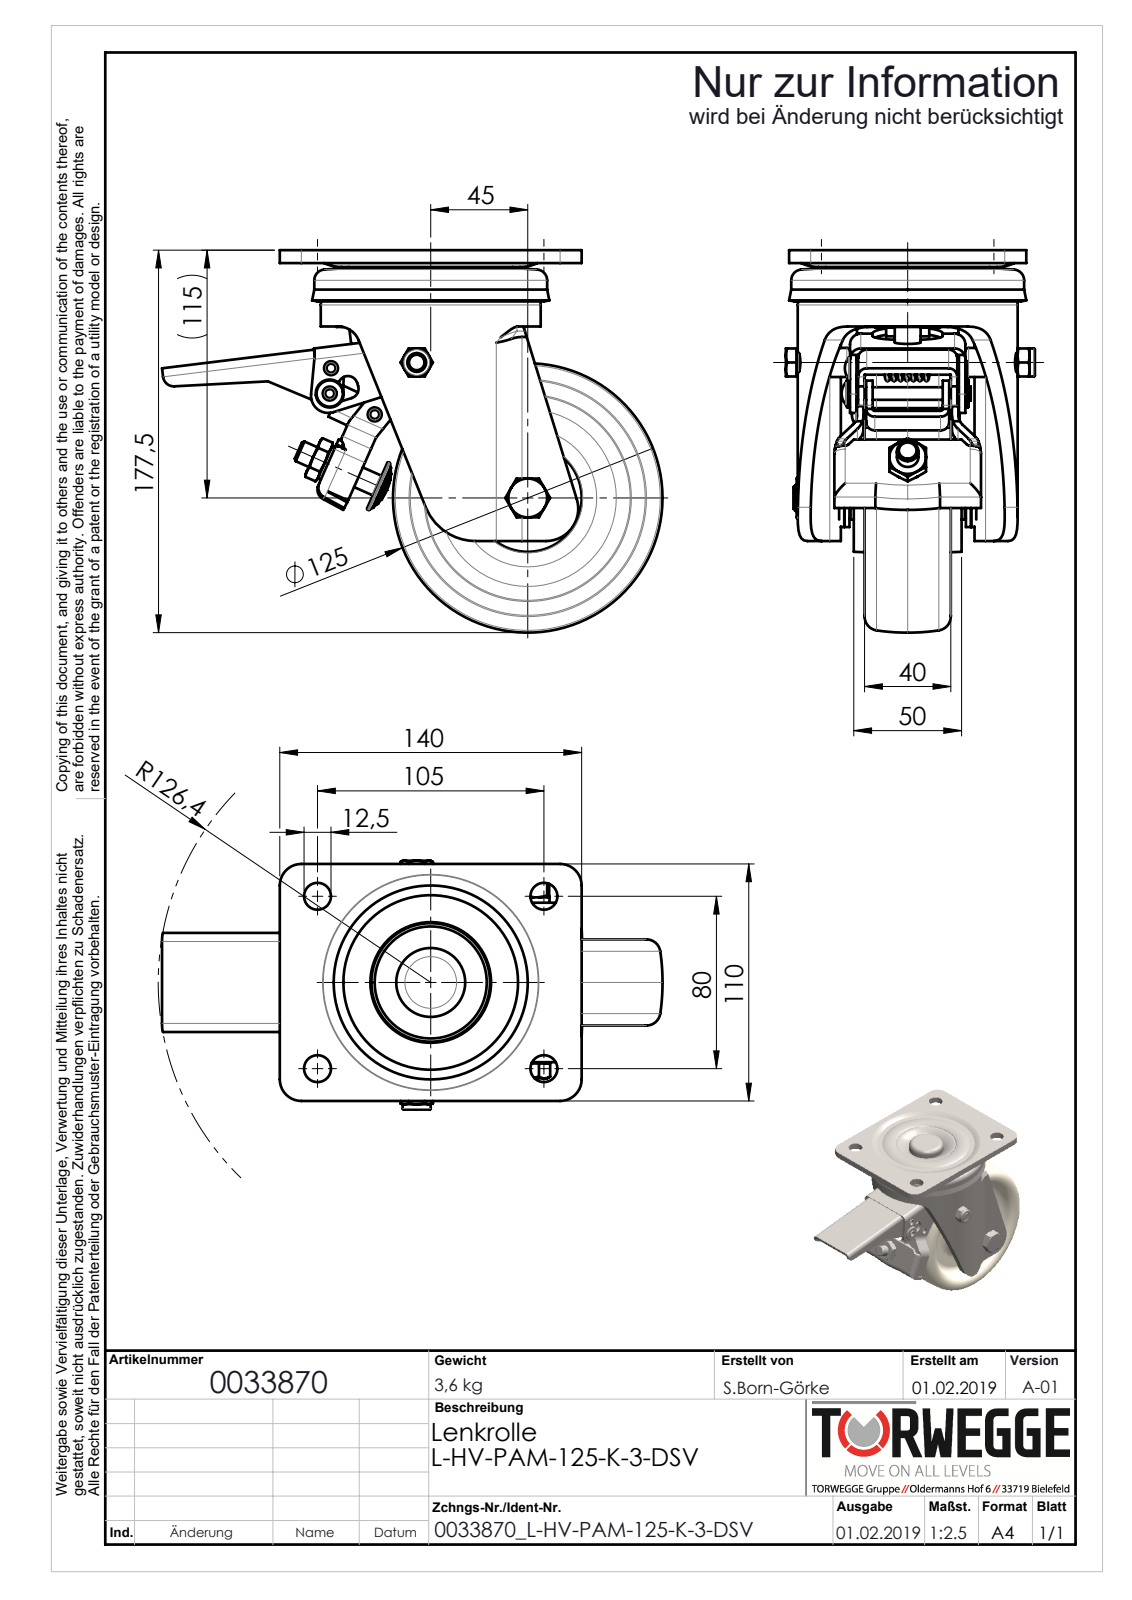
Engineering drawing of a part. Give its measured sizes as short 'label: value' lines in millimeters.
name: 0033870_L-HV-PAM-125-K-3-DSV_(A-01)
written by: SolidWorks 2018 (AUTOMOTIVE_DESIGN)
unit: mm
bodies: 0 solids, 953 faces (290 planar, 314 cylindrical, 349 other)
size: 232.11 × 177.5 × 115.5
holes: 4× ⌀12.5, 3× ⌀4.2, 3× ⌀6.2, 1× ⌀6.15, 1× ⌀6.4, 1× ⌀8.2, 1× ⌀8.4, 1× ⌀8.5, 1× ⌀9.2, 1× ⌀10.2, 1× ⌀12.2, 1× ⌀13
bosses: 3× ⌀10.1, 3× ⌀6.5, 3× ⌀5.85, 2× ⌀20, 2× ⌀13, 2× ⌀12, 1× ⌀108, 1× ⌀102
rounds: 13× R1, 12× R5, 10× R10, 8× R1.5, 8× R2.5, 5× R15, 4× R4, 4× R6
face distances: 6, 3, 32, 30, 62, 0.54, 3.75, 46.75, 18, 26
hole spacings: 66, 23, 29.51, 80, 105, 132, 11.78, 31
